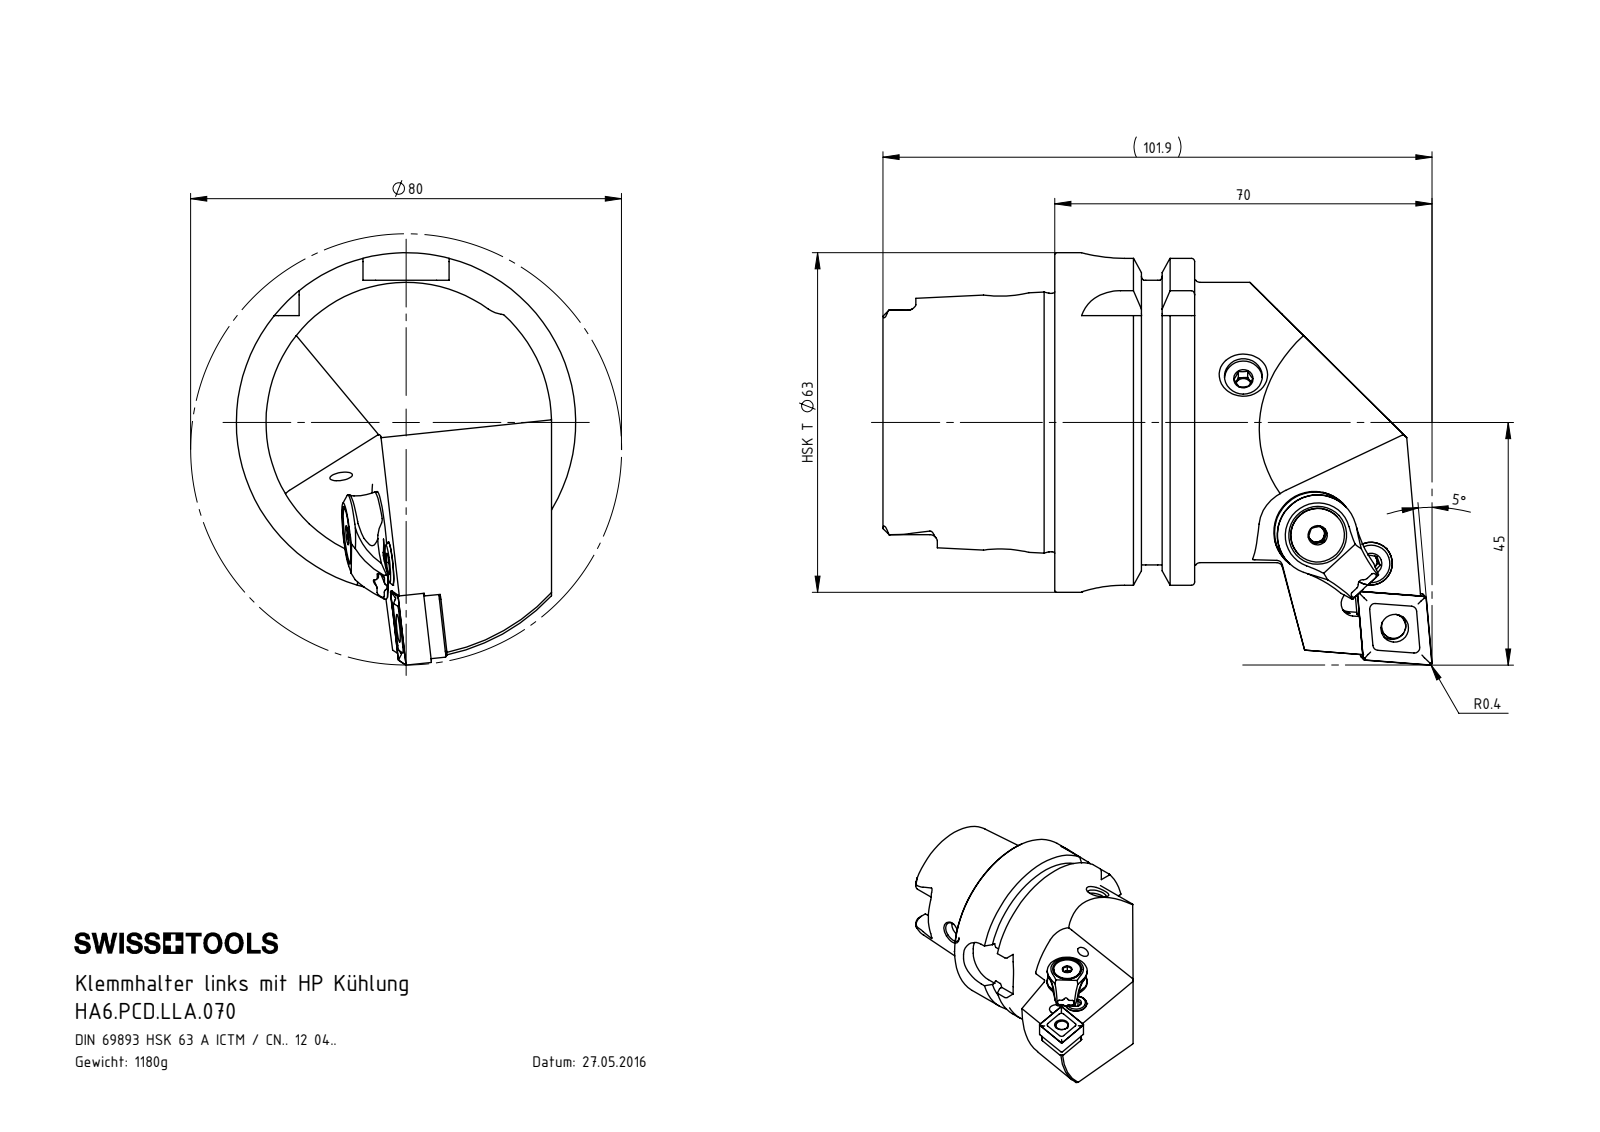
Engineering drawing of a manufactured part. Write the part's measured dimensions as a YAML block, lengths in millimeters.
part_name: "HA6.PCD.LLA.070-HP; WCD-ER3.101.000_A; CHP-ER1.015.006_A; DIN 7991 - M5x15 (+8 more)"
step_written_by: "SolidWorks 2017 (AUTOMOTIVE_DESIGN)"
units: millimeters
bodies: {solids: 10, faces: 473, planar: 156, cylindrical: 130, other: 187}
overall_size: [101.9, 76.5, 63]
volume: 149415
surface_area: 35401
round_holes:
  - {diameter: 4.2, count: 3}
  - {diameter: 7, count: 2}
  - {diameter: 8.4, count: 2}
  - {diameter: 1.2, count: 1}
  - {diameter: 2, count: 1}
  - {diameter: 2.5, count: 1}
  - {diameter: 3, count: 1}
  - {diameter: 5, count: 1}
  - {diameter: 5.16, count: 1}
  - {diameter: 5.2, count: 1}
  - {diameter: 6.4, count: 1}
  - {diameter: 7.5, count: 1}
round_bosses_or_shafts:
  - {diameter: 8, count: 2}
  - {diameter: 63, count: 1}
  - {diameter: 54.95, count: 1}
  - {diameter: 52, count: 1}
  - {diameter: 47.94, count: 1}
  - {diameter: 15, count: 1}
  - {diameter: 13.4, count: 1}
  - {diameter: 10, count: 1}
partial_cylinders:
  - {radius: 1.4, count: 6}
  - {radius: 0.4, count: 4}
  - {radius: 1, count: 4}
  - {radius: 8, count: 4}
  - {radius: 0.5, count: 2}
  - {radius: 2.5, count: 2}
  - {radius: 2.82, count: 2}
  - {radius: 2.88, count: 2}
face_to_face_distances: [25.95, 16, 9.95, 31.9, 41.85, 57.85, 52.8, 21.8, 11.85, 4.5]
hole_center_spacings: [4.5, 10.43, 12.22, 20.03, 20.09, 23.5, 23.56, 12.8]
